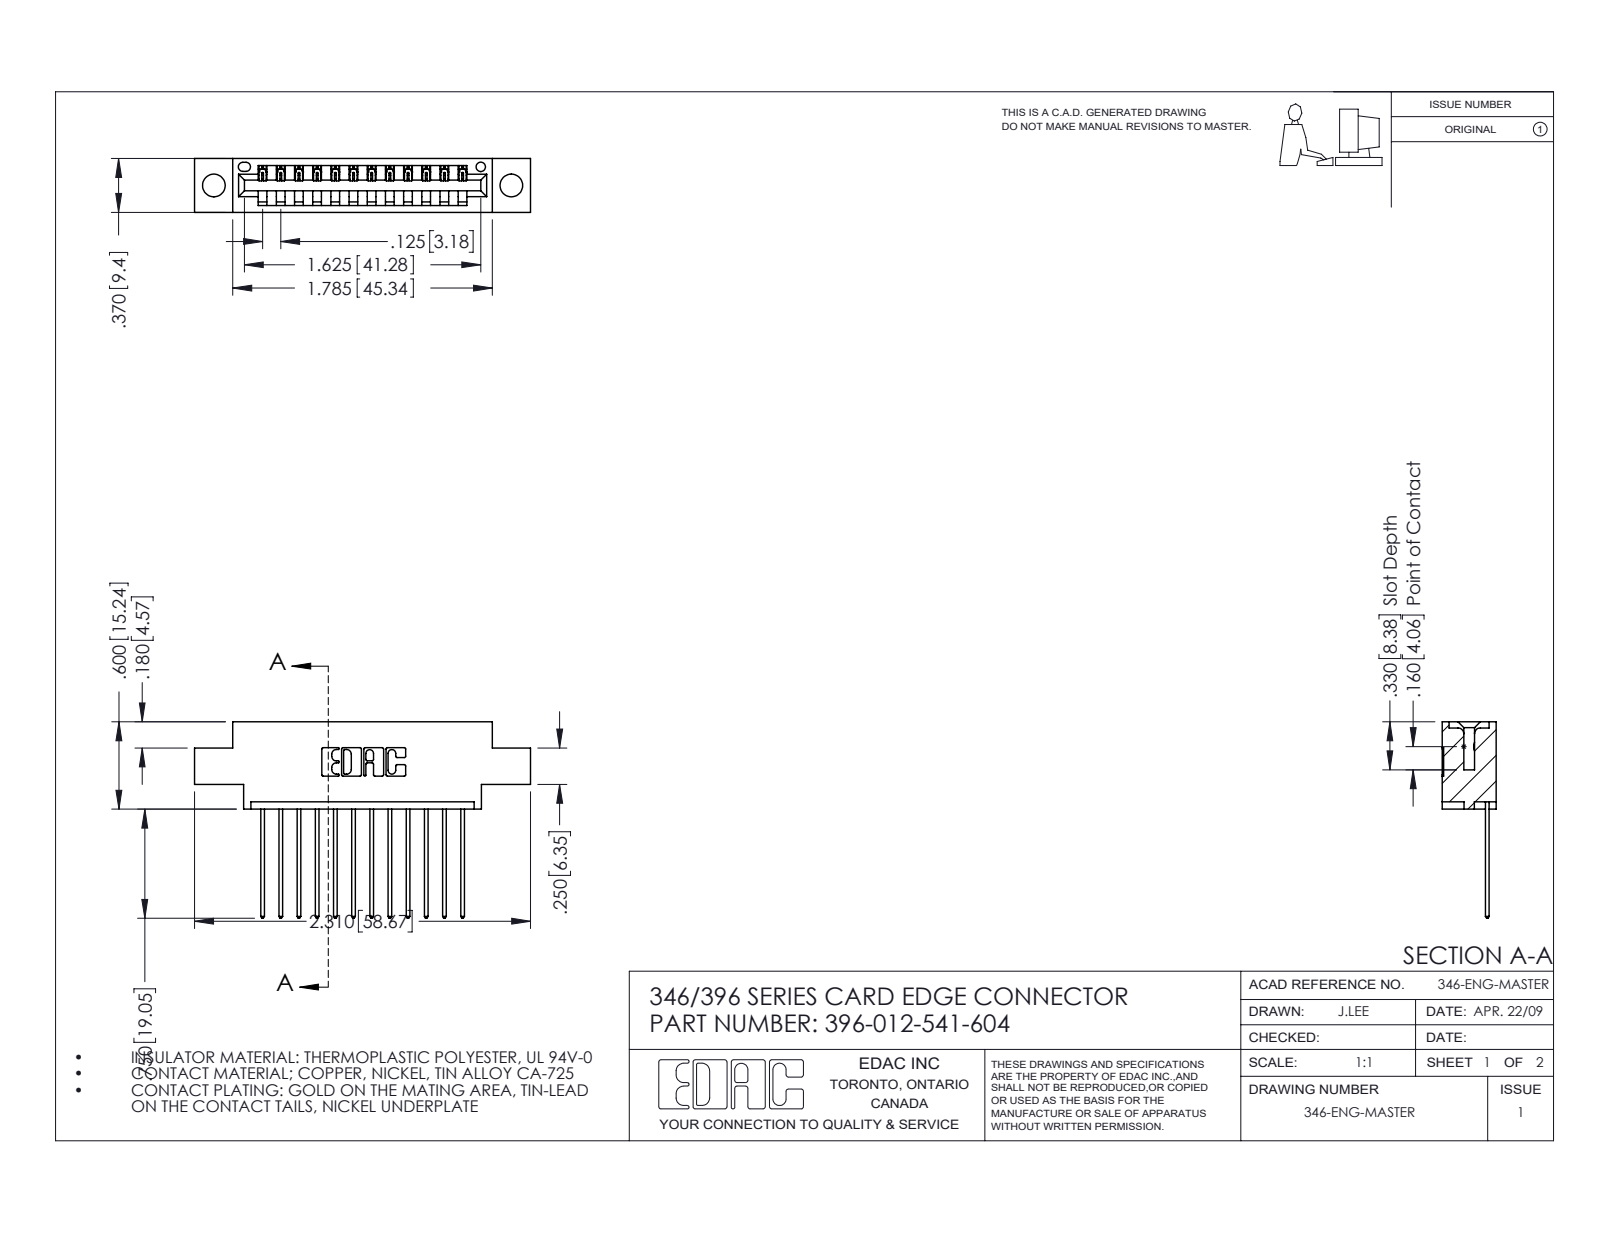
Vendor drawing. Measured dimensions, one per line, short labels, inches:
name: 396-012-541-604; 345-292-001_345-293-141; 346 Part_0.170 Offset - 0.156 Dia-TH
written by: SolidWorks 2016 (CONFIG_CONTROL_DESIGN)
unit: in
bodies: 13 solids, 822 faces (560 planar, 262 cylindrical, 0 other)
size: 2.31 × 1.35 × 0.37
volume: 0.318 in³; area: 9.898 in²
holes: 2× ⌀0.156, 1× ⌀0.064
rounds: 24× R0.006, 24× R0.01, 22× R0.01, 6× R0.007, 6× R0.031, 3× R0.026, 2× R0.031, 2× R0.04
face distances: 0.25, 0.048, 0.322, 0.37, 0.072, 0.298, 0.025, 0.148, 0.222, 0.1
hole spacings: 0.246, 1.839, 2.045
